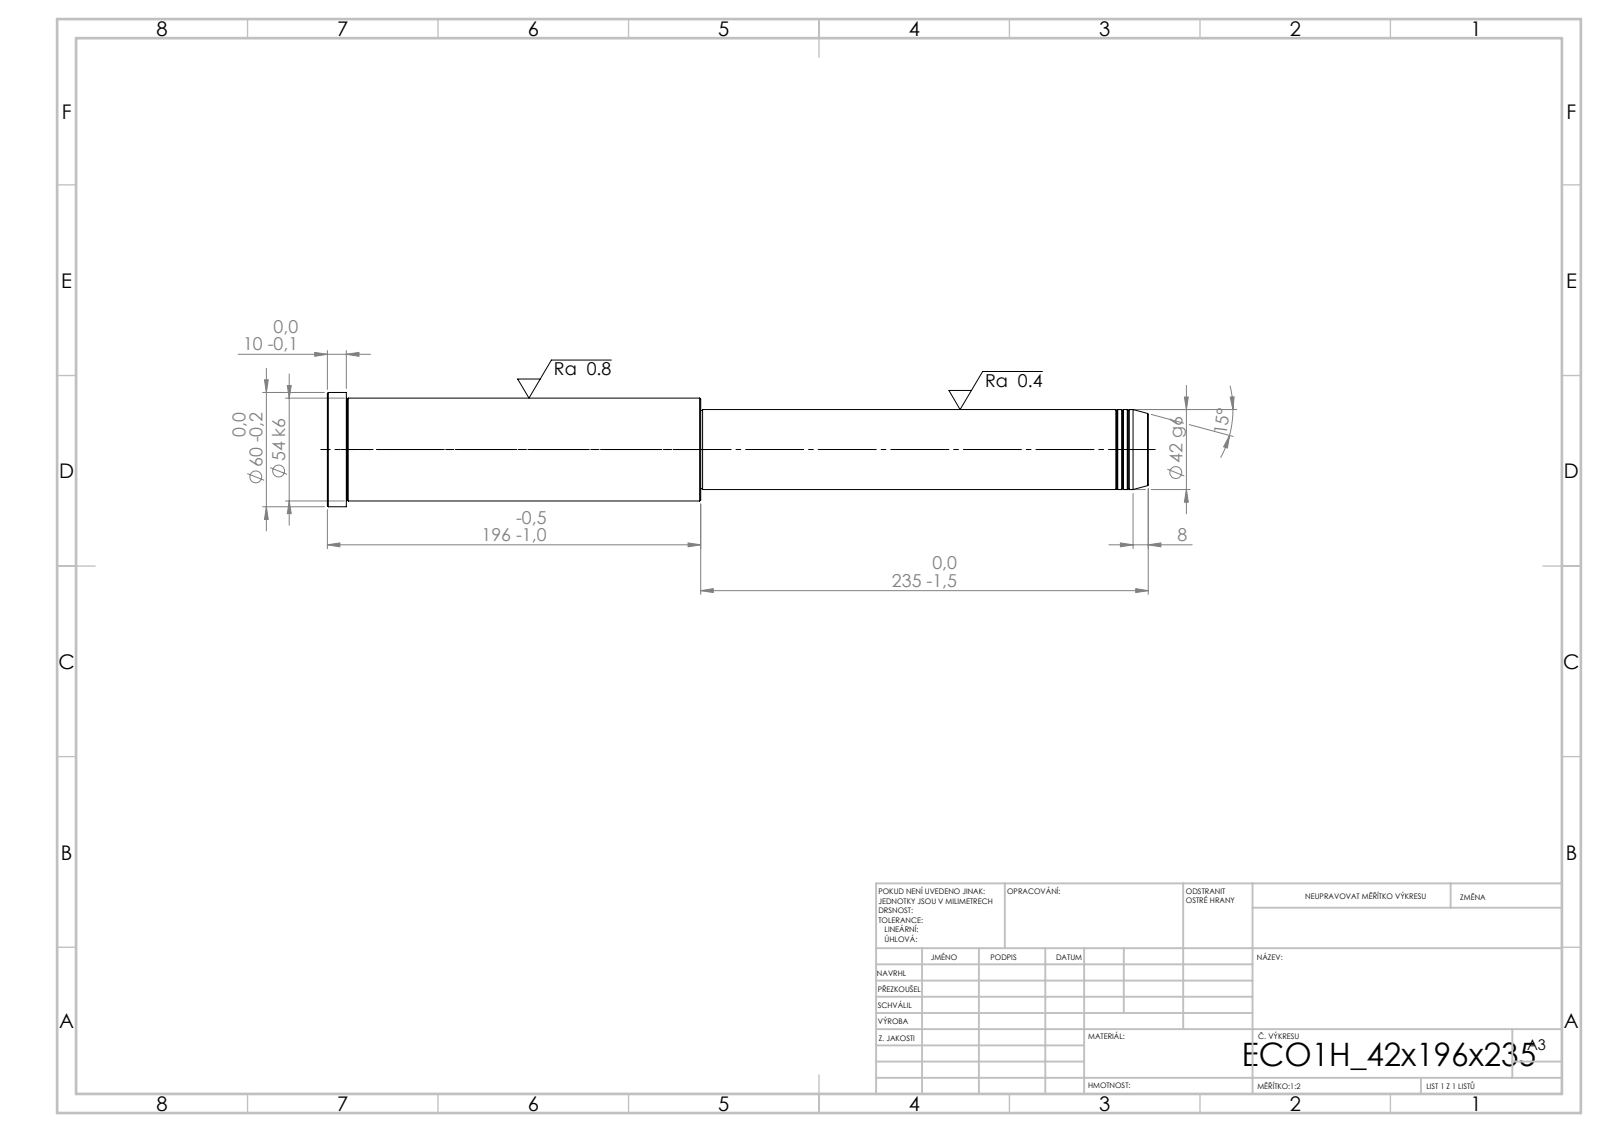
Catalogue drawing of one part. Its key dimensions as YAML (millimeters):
step_written_by: "SolidWorks 2019 (CONFIG_CONTROL_DESIGN)"
units: millimeters
bodies: {solids: 1, faces: 43, planar: 5, cylindrical: 14, other: 24}
overall_size: [431, 60, 60]
volume: 778409
surface_area: 70133
round_bosses_or_shafts:
  - {diameter: 60, count: 1}
  - {diameter: 54, count: 1}
  - {diameter: 42, count: 1}
  - {diameter: 41, count: 1}
face_to_face_distances: [431, 235, 196, 421, 186, 10, 234, 1, 187, 197]
